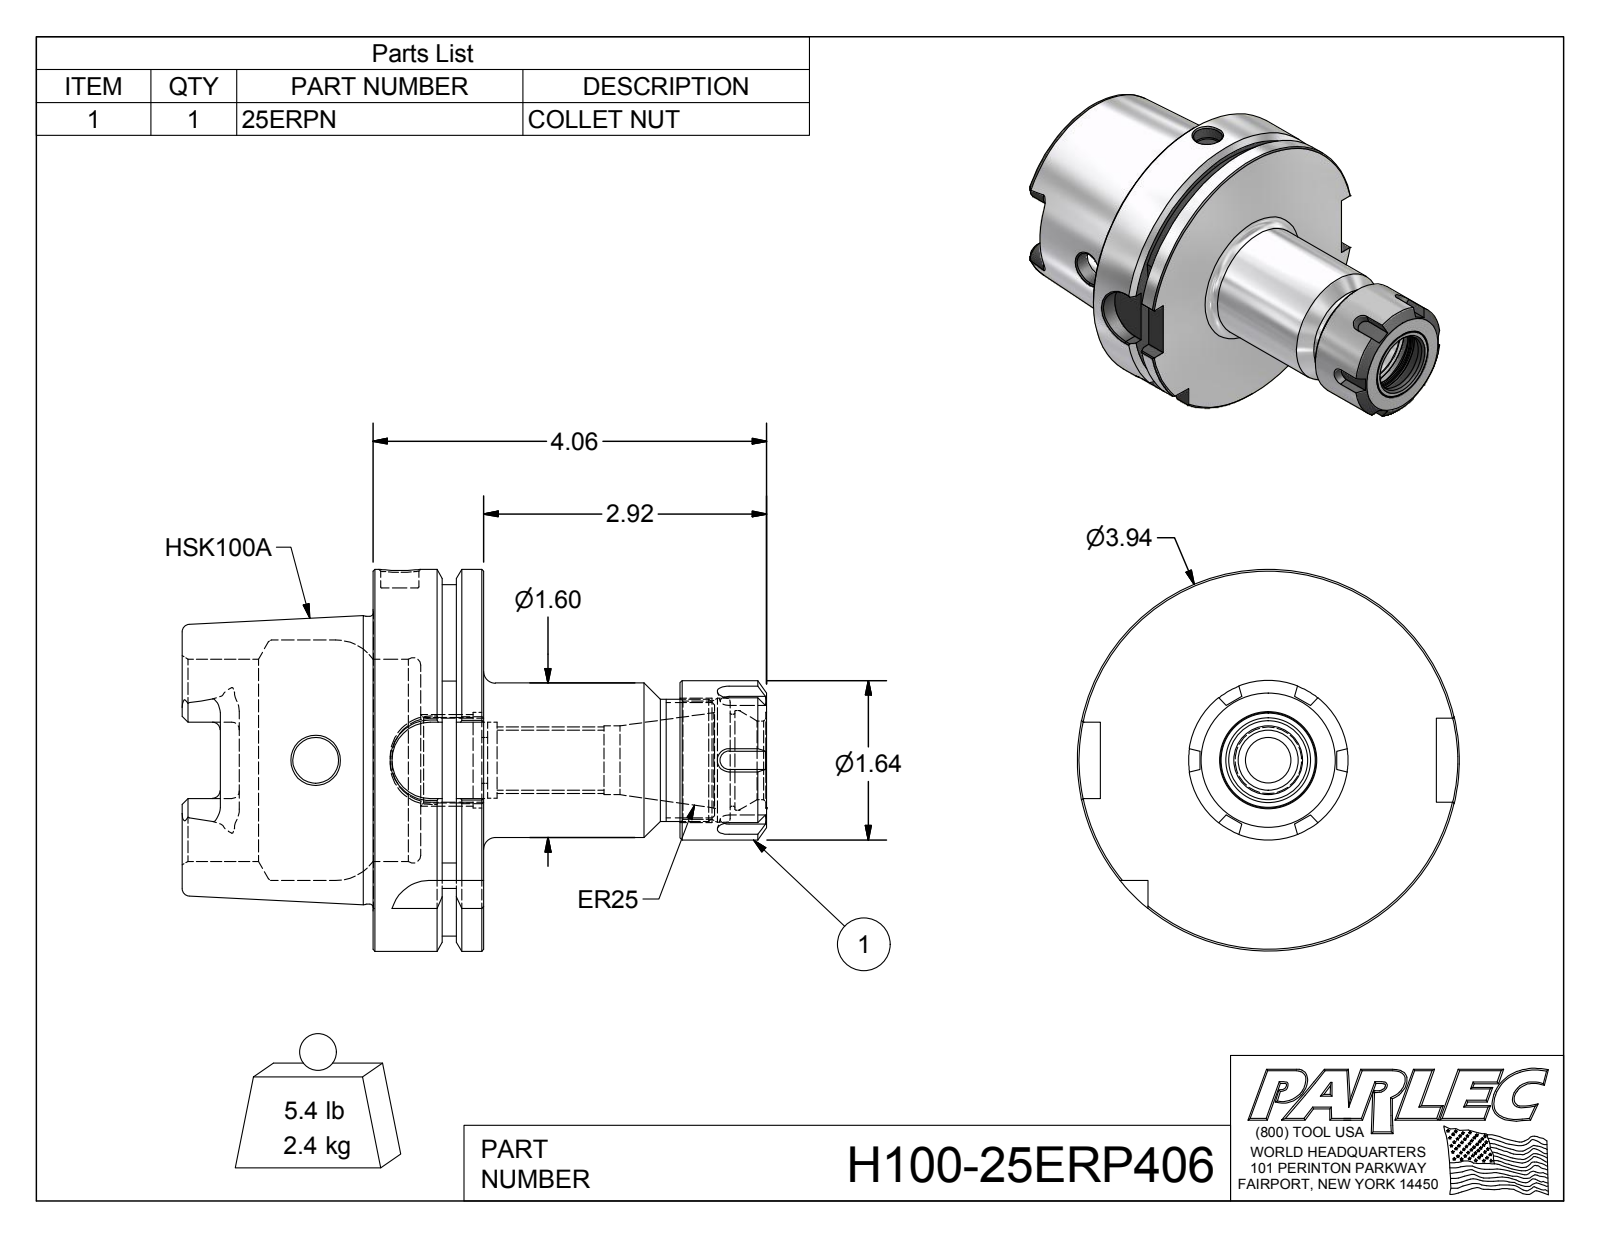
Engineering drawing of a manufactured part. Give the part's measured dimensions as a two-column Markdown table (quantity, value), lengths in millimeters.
| quantity | value |
| --- | --- |
| part name | H100-25ERP406; H100-25ER4-1; 25ERPN |
| STEP written by | Autodesk Inventor 2012 (AUTOMOTIVE_DESIGN) |
| units | millimeters |
| bodies | 2 solids, 180 faces (69 planar, 43 cylindrical, 68 other) |
| overall size | 153.1 × 100 × 100 |
| volume | 322 700 mm³ |
| surface area | 67 160 mm² |
| round holes (diameter × count) | 12 × 2, 10 × 1, 12 × 1, 15.7 × 1, 18 × 1, 19.9 × 1, 20.6 × 1, 22.4 × 1, 24.1 × 1, 25 × 1, 26.1 × 1, 30.9 × 1 |
| round bosses / shafts (diameter × count) | 100 × 1, 75.4 × 1, 41.7 × 1, 40.5 × 1, 32 × 1 |
| partial cylindrical surfaces (radius × count) | 2 × 6, 4.9 × 4, 10 × 4, 46 × 1 |
| main face-to-face distances | 29, 12.5, 16.5, 50, 62.5, 79, 71.9, 21.9, 9.4, 7.1 |
